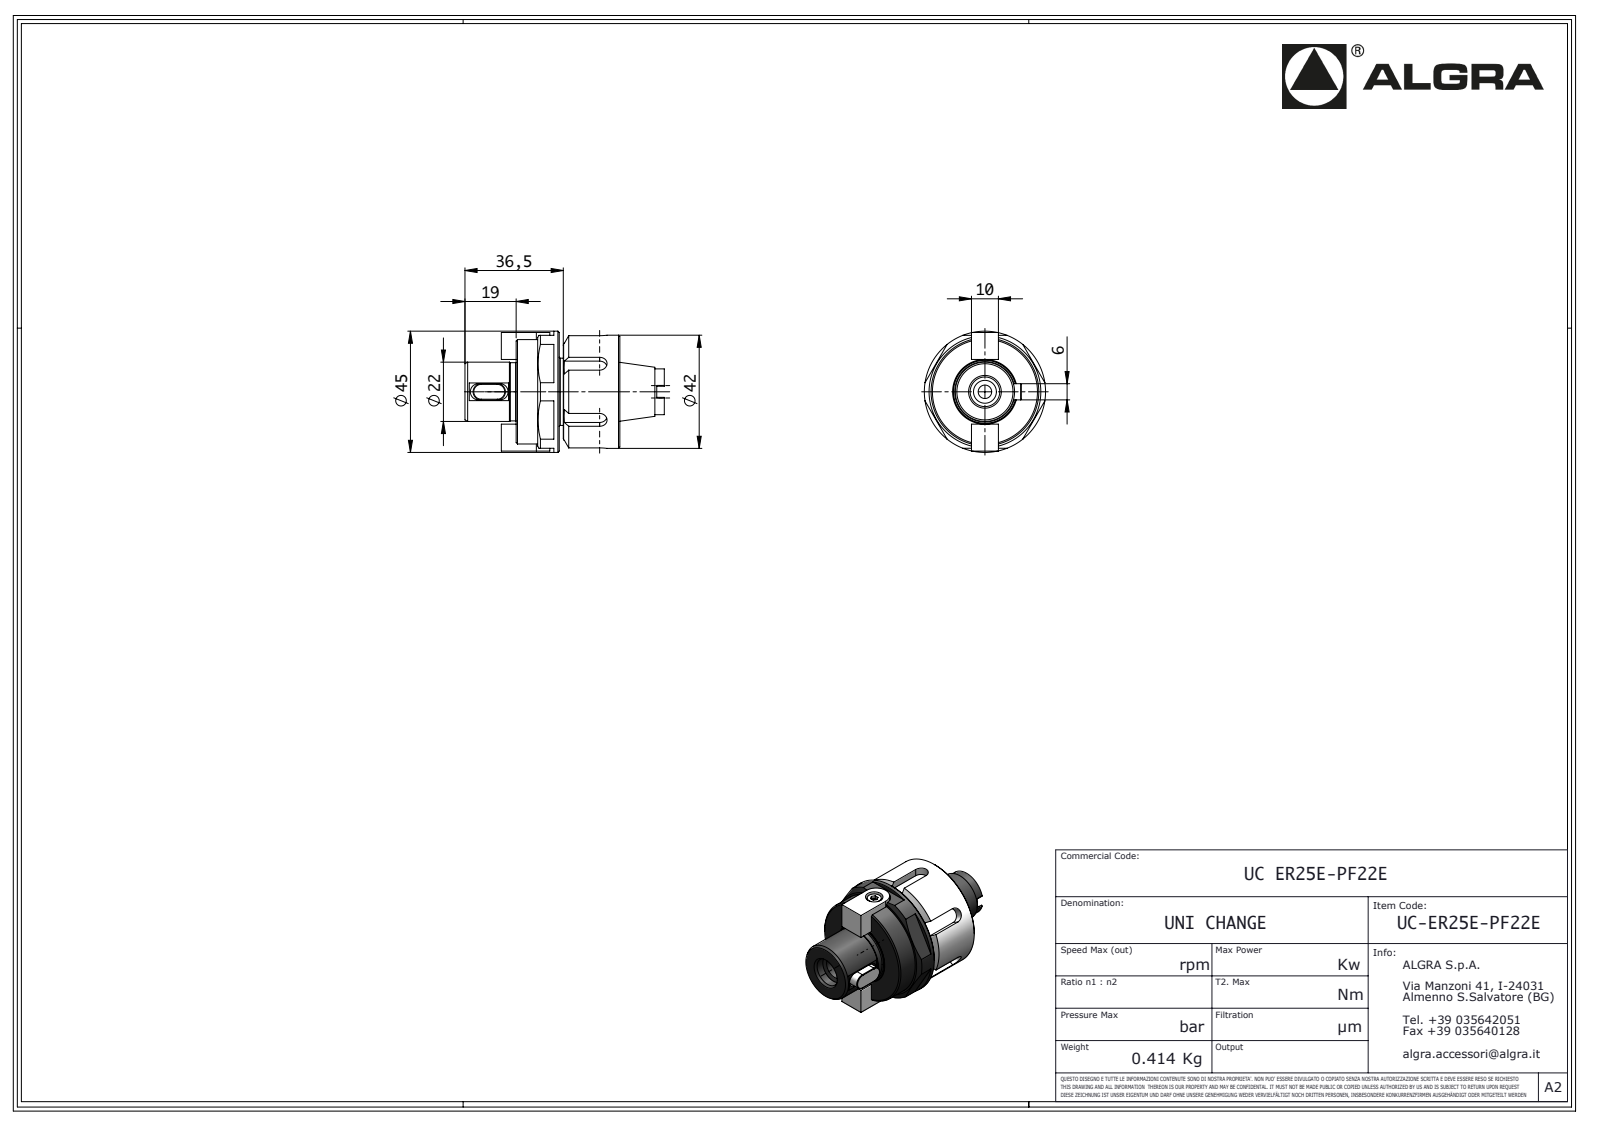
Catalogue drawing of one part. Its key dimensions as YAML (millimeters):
part_name: "UC-ER25E-PF22E"
step_written_by: "SolidWorks 2016 (AUTOMOTIVE_DESIGN)"
units: millimeters
bodies: {solids: 0, faces: 152, planar: 85, cylindrical: 44, other: 23}
overall_size: [74, 45, 45]
round_holes:
  - {diameter: 2.5, count: 2}
  - {diameter: 5, count: 1}
  - {diameter: 6.5, count: 1}
  - {diameter: 8.5, count: 1}
  - {diameter: 11, count: 1}
  - {diameter: 30.5, count: 1}
  - {diameter: 32.4, count: 1}
round_bosses_or_shafts:
  - {diameter: 45, count: 1}
  - {diameter: 42, count: 1}
  - {diameter: 40, count: 1}
  - {diameter: 22, count: 1}
  - {diameter: 21.6, count: 1}
  - {diameter: 17, count: 1}
  - {diameter: 5.5, count: 1}
partial_cylinders:
  - {radius: 0.24, count: 4}
  - {radius: 3, count: 4}
  - {radius: 2.75, count: 3}
  - {radius: 0.25, count: 2}
  - {radius: 3.81, count: 2}
  - {radius: 5, count: 2}
  - {radius: 5.05, count: 1}
face_to_face_distances: [16, 10, 22.5, 38.5, 2.95, 38.95, 5.5, 13, 9.5, 44]
hole_center_spacings: [5.25, 10.5]
